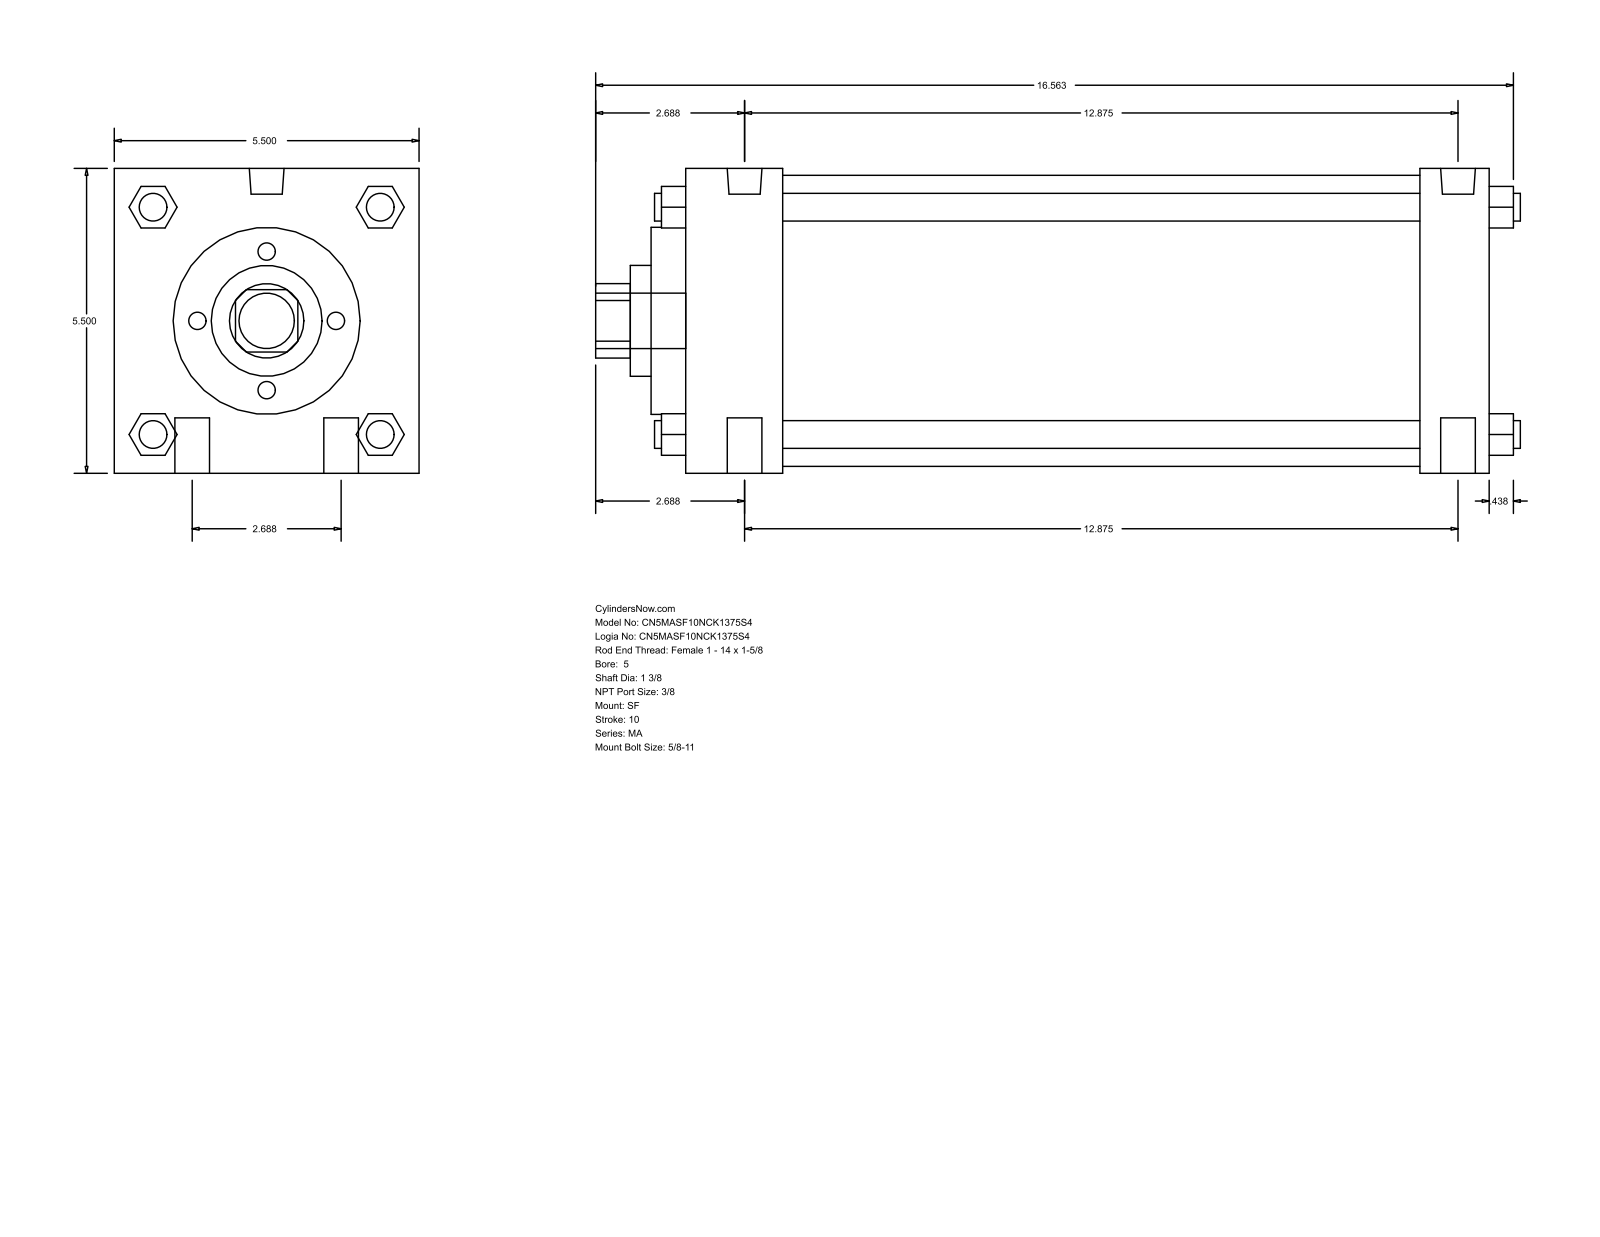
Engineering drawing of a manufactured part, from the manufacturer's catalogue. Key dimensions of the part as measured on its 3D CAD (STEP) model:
Part name (STEP PRODUCT): MA_SF__0500_1.375
STEP written by: GSSL Pune (CONFIG_CONTROL_DESIGN)
Units: millimetres
Bodies: 0 solids, 126 faces (95 planar, 31 cylindrical, 0 other)
Overall size (bounding box): 423.86 × 139.7 × 139.7
Round holes (diameter × count): ⌀34.92 ×1, ⌀50.8 ×1, ⌀85.72 ×1, ⌀133.35 ×1
Round bosses / shafts (diameter × count): ⌀15.88 ×4, ⌀12.7 ×4, ⌀15.93 ×2, ⌀11.11 ×2, ⌀25.4 ×1
Partial cylindrical surfaces — rounded edges, fillets, slot ends (radius × count): R17.06 ×1
Main face-to-face distances: 139.7, 368.3, 44.45, 336.55, 292.1, 323.85, 31.75, 15.87, 60.32, 352.42
